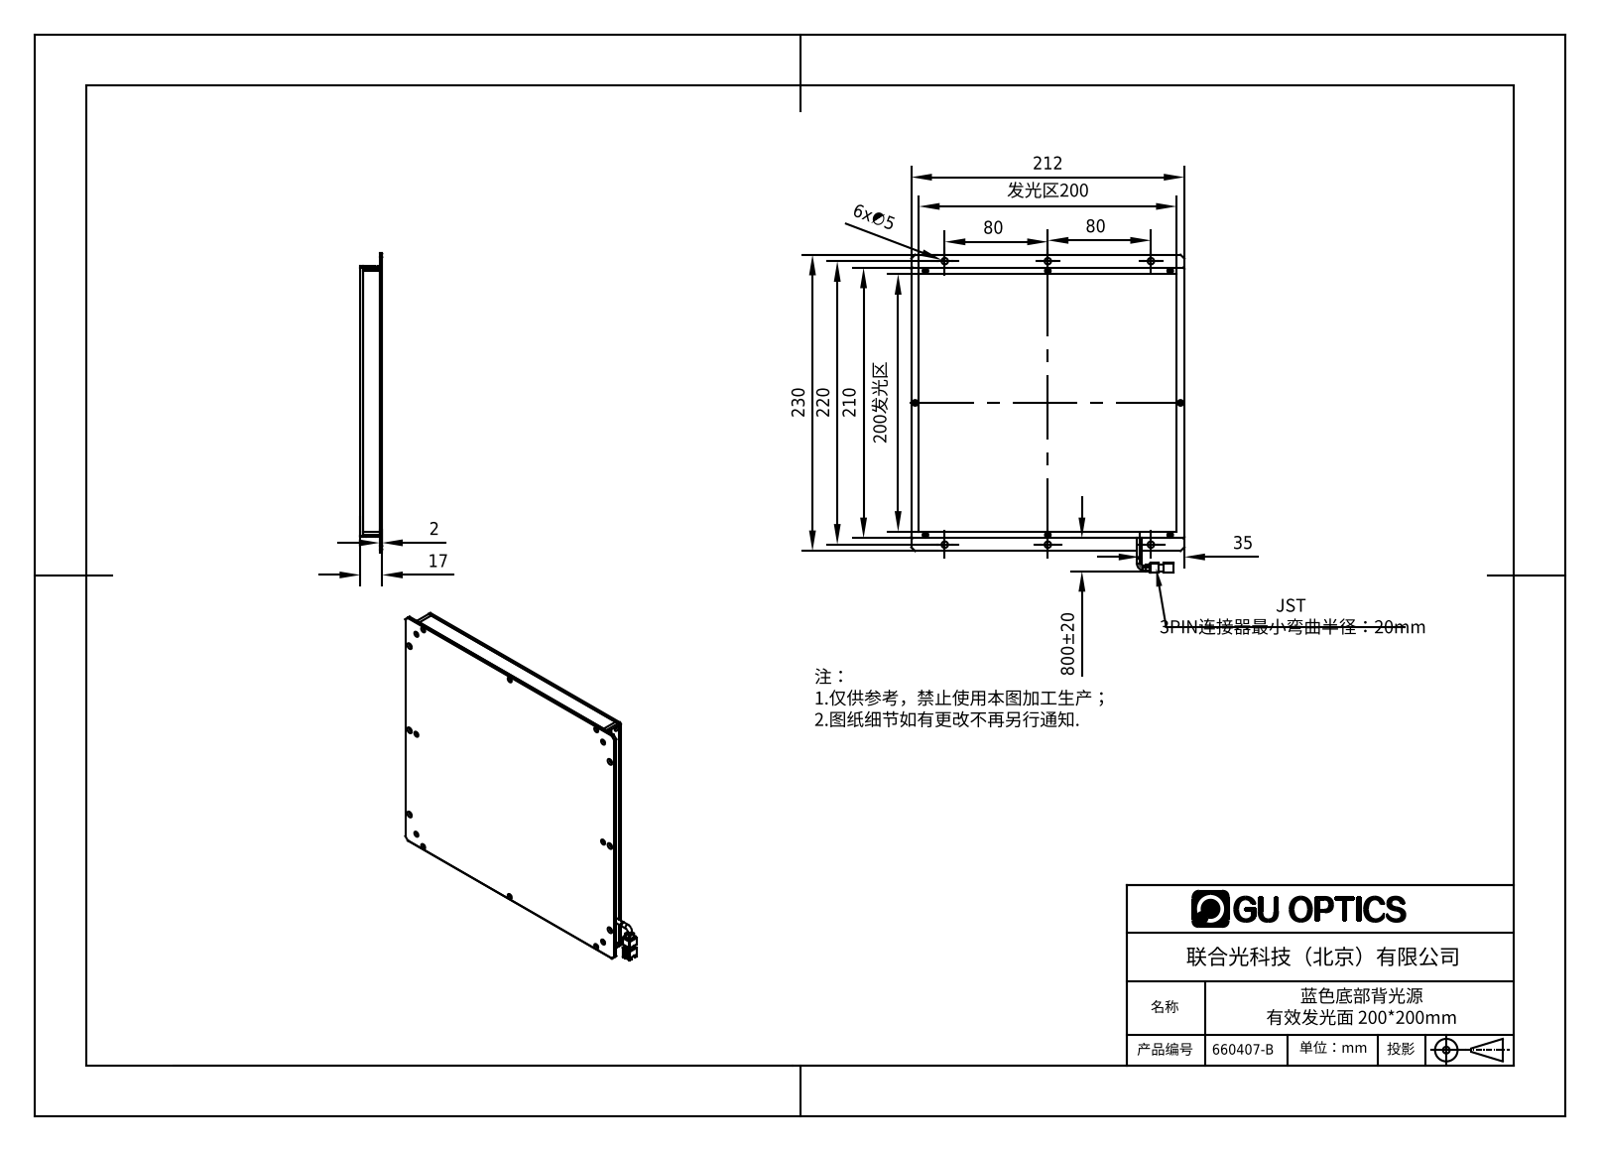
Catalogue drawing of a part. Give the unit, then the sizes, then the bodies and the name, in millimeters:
Units: millimetres
Overall size (bounding box): 247 × 212 × 20.3
Round holes (diameter × count): ⌀1.6 ×16, ⌀2.4 ×16, ⌀5 ×6
Round bosses / shafts (diameter × count): ⌀3.5 ×2
Partial cylindrical surfaces — rounded edges, fillets, slot ends (radius × count): R0.5 ×8, R1 ×4, R2 ×2, R1.6 ×1
Main face-to-face distances: 15, 2, 13, 3, 16, 18, 6, 206, 200, 5
Hole centre spacings: 95, 206, 10.97, 16.77, 27.46, 80, 80.35, 95.3
Volume: 283 962 mm³ · Surface area: 223 998 mm²
Bodies: 8 solids, 522 faces (199 planar, 149 cylindrical, 174 other)
Part name (STEP PRODUCT): 660407-B
STEP written by: SolidWorks 2016 (AUTOMOTIVE_DESIGN)
